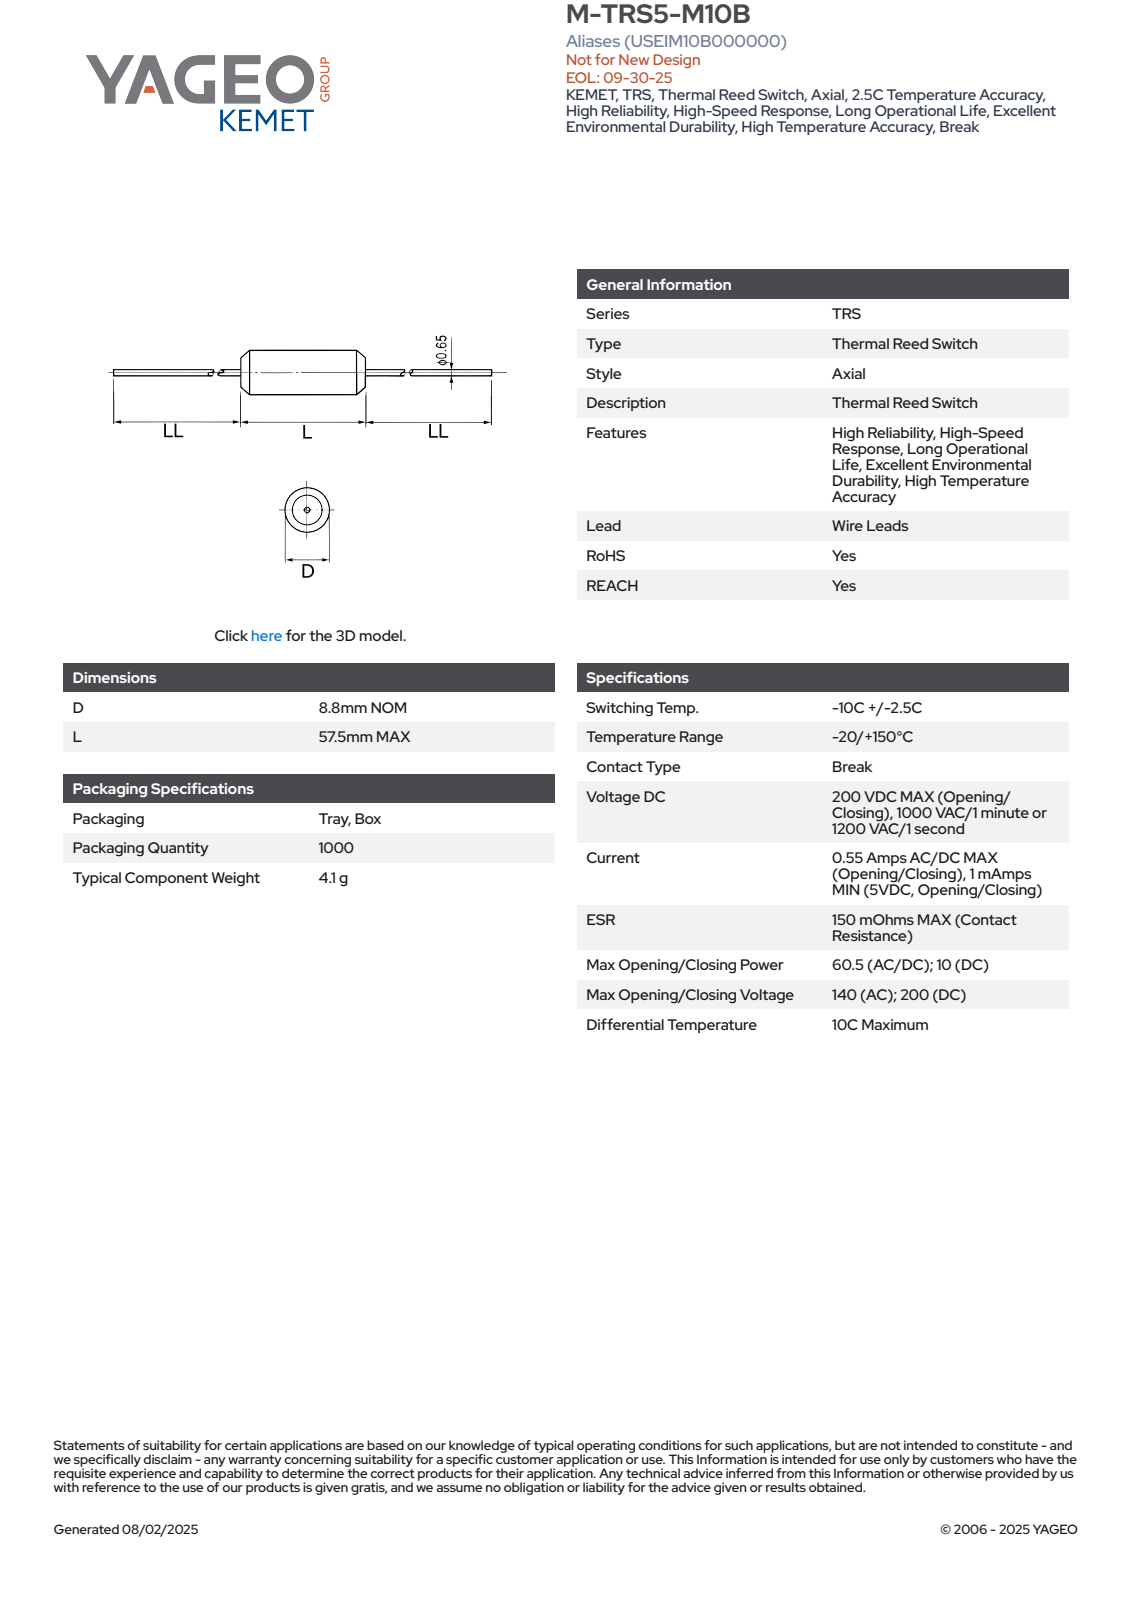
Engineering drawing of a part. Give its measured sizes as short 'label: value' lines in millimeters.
name: Default
written by: SolidWorks 2014 (AUTOMOTIVE_DESIGN)
unit: mm
bodies: 1 solid, 85 faces (26 planar, 24 cylindrical, 35 other)
size: 57.5 × 8.8 × 8.8
volume: 1 504 mm³; area: 838 mm²
bosses: 1× ⌀8.8, 1× ⌀0.65
rounds: 1× R4.39
face distances: 25.5, 16, 41.5, 57.5
